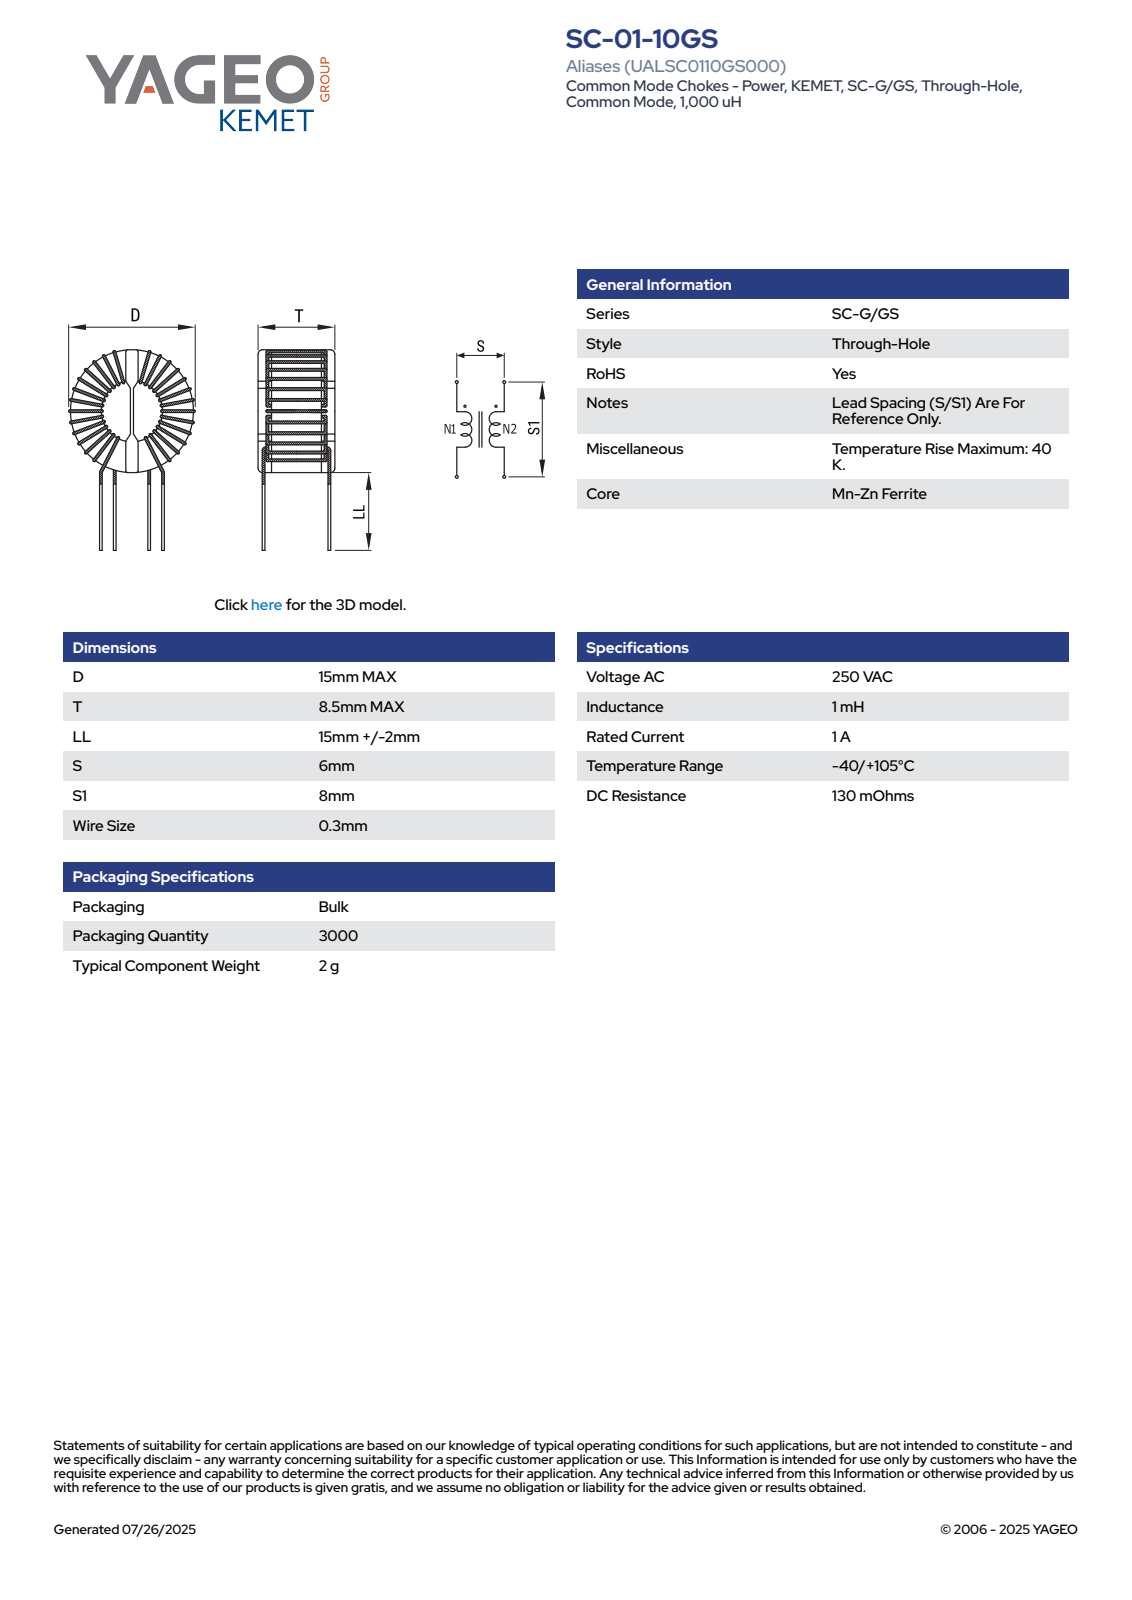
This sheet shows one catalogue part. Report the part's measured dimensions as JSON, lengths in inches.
{"part_name": "SC-01-10GS", "step_written_by": "SolidWorks 2018 (AUTOMOTIVE_DESIGN)", "units": "inches", "bodies": {"solids": 1, "faces": 279, "planar": 119, "cylindrical": 77, "other": 83}, "overall_size": [1.118, 0.591, 0.335], "volume_in3": 0.062, "surface_area_in2": 1.598, "round_bosses_or_shafts": [[0.012, 8], [0.012, 1]], "partial_cylinders_radius": [[0.006, 16], [0.084, 1], [0.095, 1], [0.105, 1], [0.115, 1], [0.118, 1], [0.217, 1], [0.22, 1]], "face_to_face_distances": [0.033, 0.301, 0.047, 0.079, 0.268, 0.126, 0.031, 0.335, 0.045, 0.081]}
